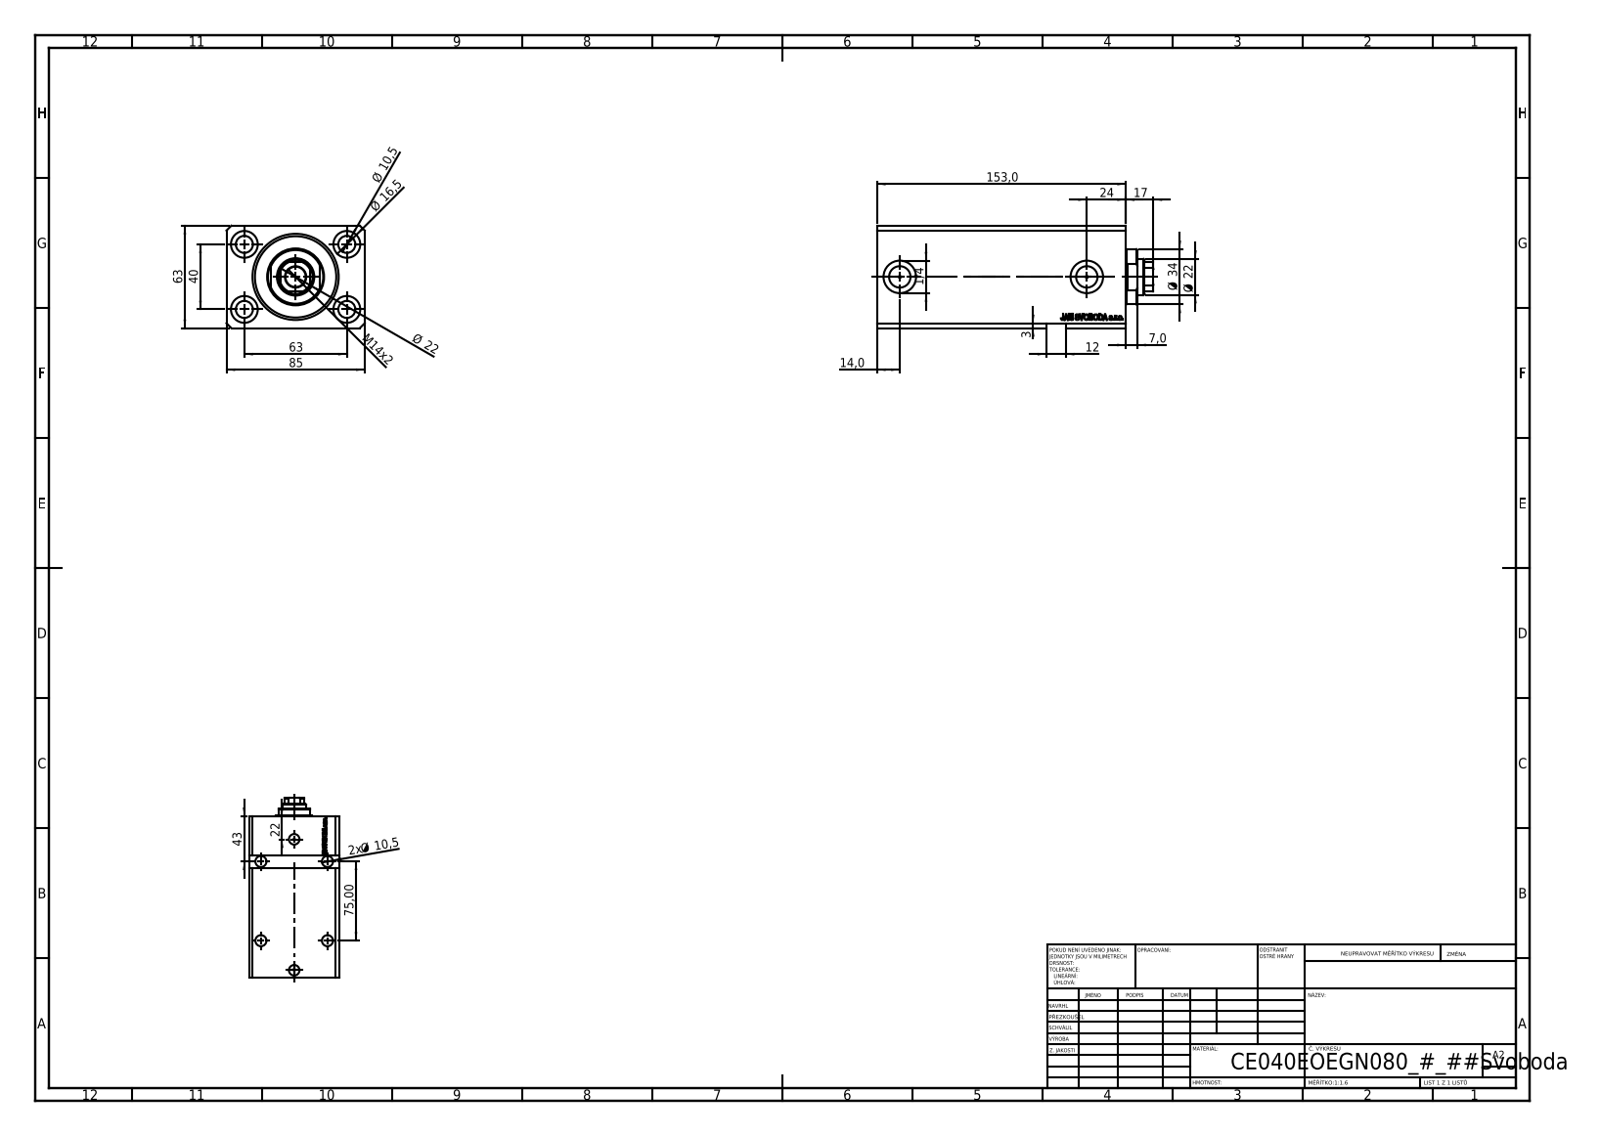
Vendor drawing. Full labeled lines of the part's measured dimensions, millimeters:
Part name (STEP PRODUCT): V250CE_VC_E; V250CE_E_Body; V250CE_C_VCP
STEP written by: SolidWorks 2019 (CONFIG_CONTROL_DESIGN)
Units: millimetres
Bodies: 3 solids, 937 faces (459 planar, 104 cylindrical, 374 other)
Overall size (bounding box): 170 × 85 × 63
Volume: 666 198 mm³ · Surface area: 126 235 mm²
Round holes (diameter × count): ⌀10.5 ×8, ⌀1.25 ×4, ⌀16.5 ×4, ⌀10 ×2, ⌀13.16 ×2, ⌀20 ×2, ⌀12.5 ×1, ⌀22 ×1, ⌀40 ×1, ⌀53 ×1
Round bosses / shafts (diameter × count): ⌀34 ×1
Partial cylindrical surfaces — rounded edges, fillets, slot ends (radius × count): R10.5 ×1
Main face-to-face distances: 63, 85, 153, 17, 136, 11.4, 124.6, 141.6, 56, 60
Hole centre spacings: 37.31, 63, 37.86, 40, 41.8, 42.15, 74.63, 75
